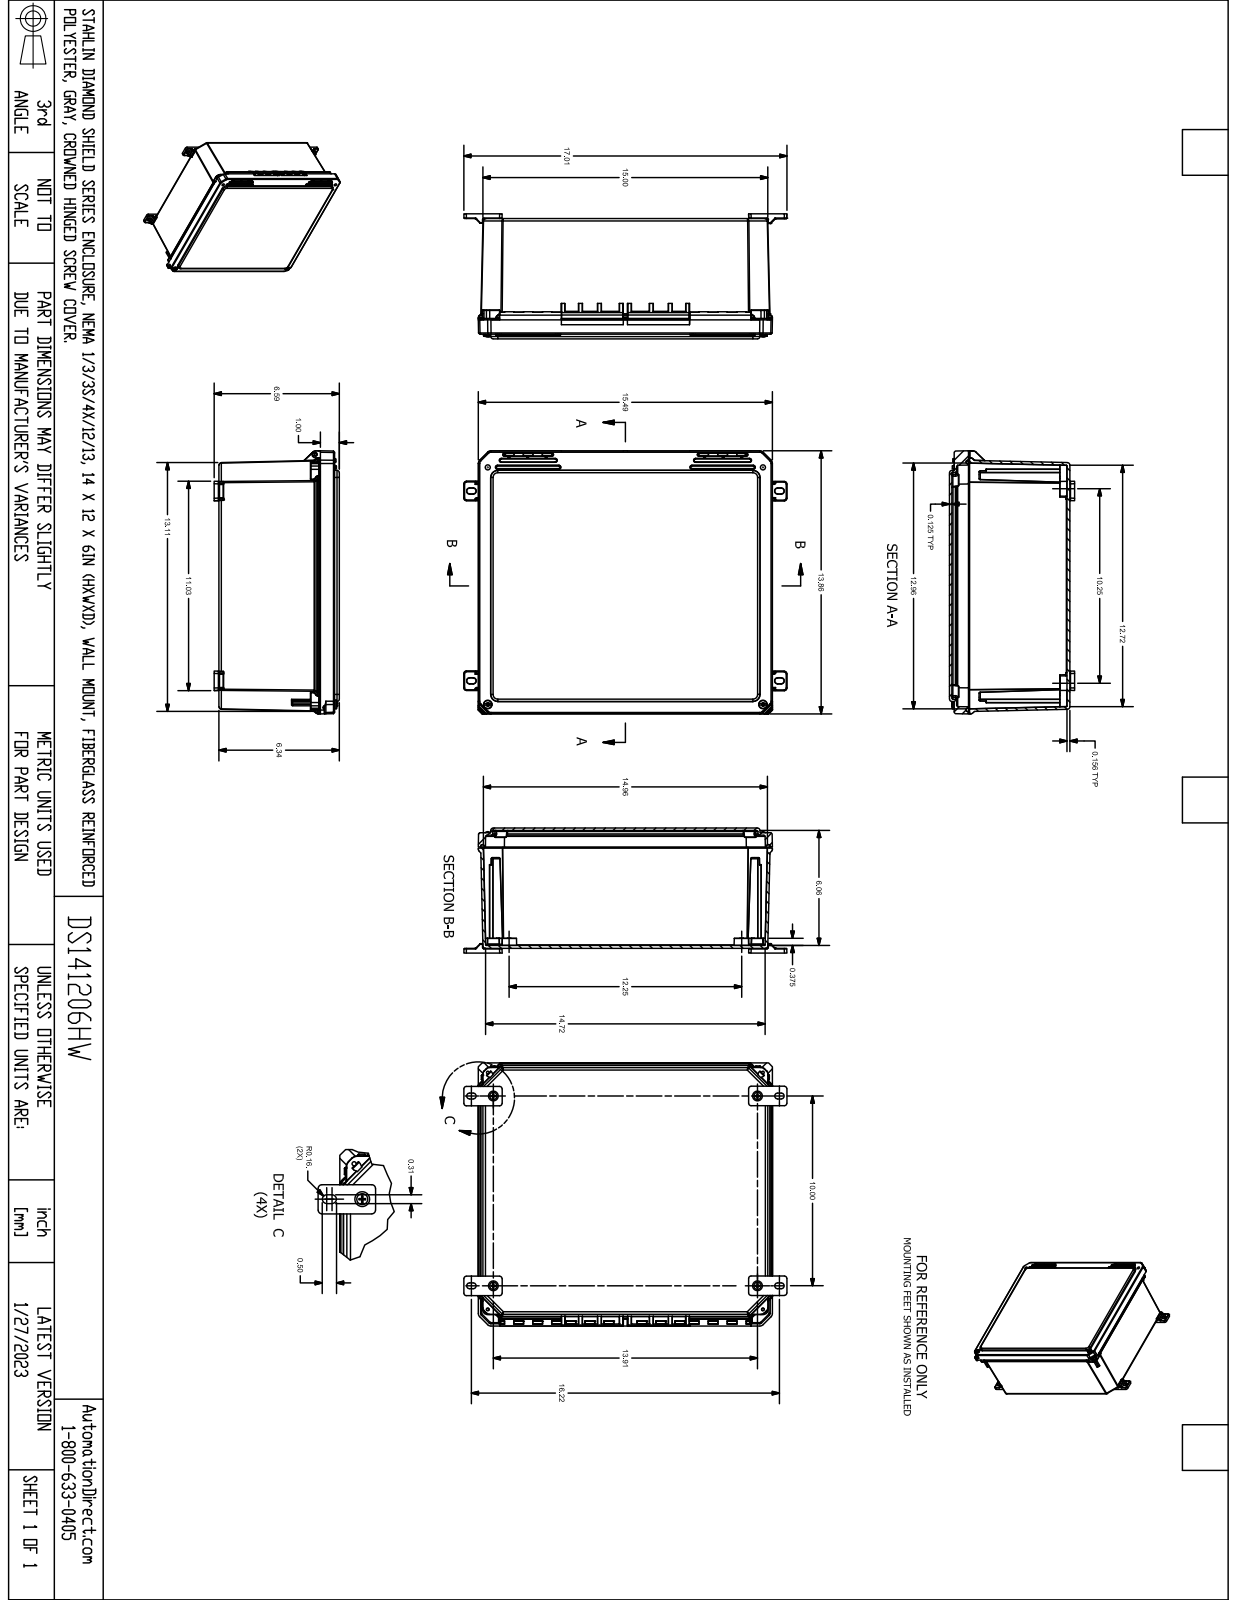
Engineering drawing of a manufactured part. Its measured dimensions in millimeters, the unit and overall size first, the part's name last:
Units: millimetres
Overall size (bounding box): 393.5 × 352.5 × 171.9
Round holes (diameter × count): ⌀3.9 ×8, ⌀4 ×8, ⌀4 ×4, ⌀6.4 ×4, ⌀6.4 ×4, ⌀3.5 ×3, ⌀3.8 ×2, ⌀5.6 ×2, ⌀5.8 ×2, ⌀8 ×2
Round bosses / shafts (diameter × count): ⌀6.9 ×8, ⌀22.1 ×4, ⌀6.7 ×4, ⌀11.4 ×2, ⌀11 ×2, ⌀5.3 ×2, ⌀5.1 ×2, ⌀3.4 ×2
Partial cylindrical surfaces — rounded edges, fillets, slot ends (radius × count): R0.3 ×193, R0.1 ×110, R0.5 ×54, R0.8 ×49, R0.8 ×24, R2.3 ×24, R2.4 ×24, R3.2 ×22
Main face-to-face distances: 4, 3.2, 157.1, 161, 153.9, 157.9, 3.6, 3.5, 3.5, 6.4
Hole centre spacings: 368, 362.1, 340.8, 351.4, 258.1, 368, 340.8, 40.2
Volume: 1 980 000 mm³ · Surface area: 1 035 000 mm²
Bodies: 23 solids, 2242 faces (685 planar, 894 cylindrical, 663 other)
Part name (STEP PRODUCT): FR141206HW
STEP written by: SolidWorks 2021 (AUTOMOTIVE_DESIGN)
